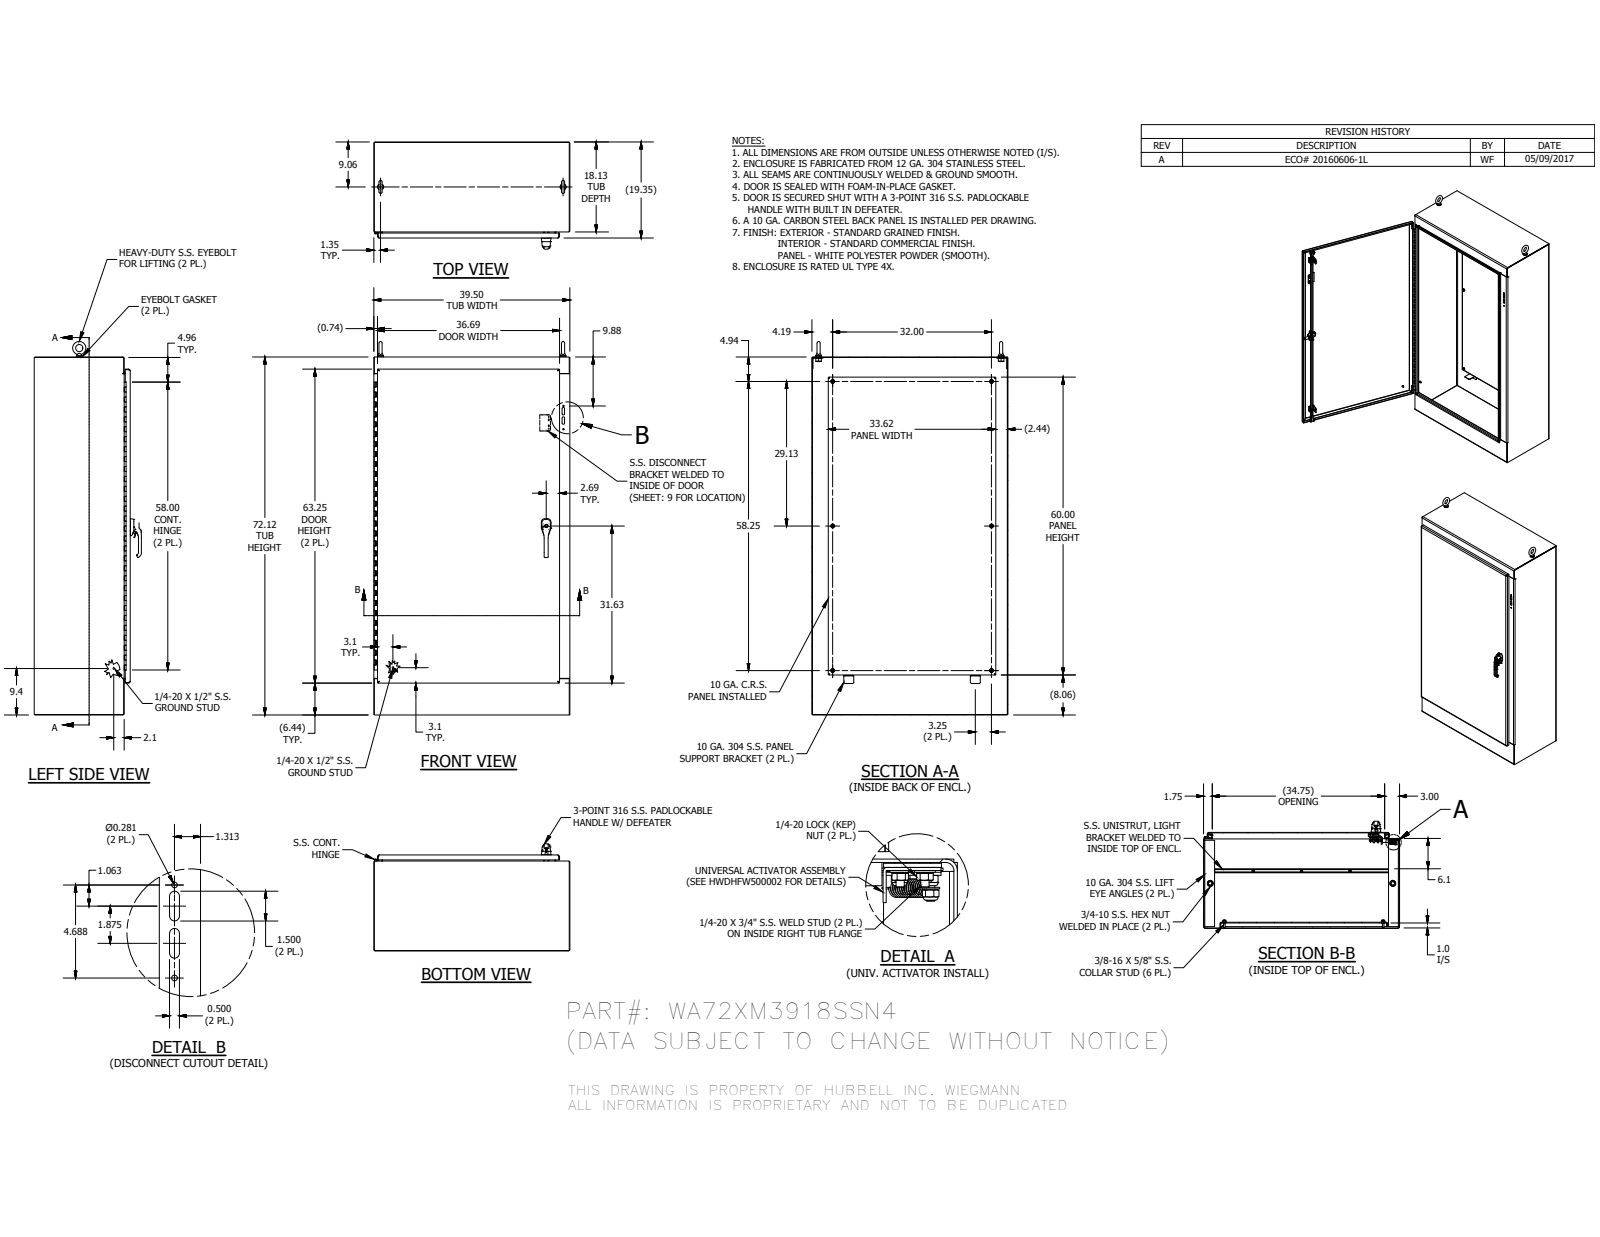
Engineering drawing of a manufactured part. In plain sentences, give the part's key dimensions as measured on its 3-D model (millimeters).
The part is named "WA72XM3918SSN4BLR; WAXM3918SSN4TOP; WAXM3918SSN4BTM; FUN00129_WAXM39SSN4 (+8 more)". Its 3-D file was written by "Autodesk Inventor 2016 (AUTOMOTIVE_DESIGN)". It is 126 solids with 4763 faces: 2197 planar, 1524 cylindrical and 1042 other. Overall it measures 1911.29 by 1003.3 by 548.55 millimeters. Its volume is 22 570 000 cubic millimeters and its surface area 16 220 000 square millimeters. Round holes: 24 of diameter 3.55, 10 of diameter 9.52, 9 of diameter 6.35, 8 of diameter 6.65, 6 of diameter 3.96, 6 of diameter 7.8, 6 of diameter 14.29, 5 of diameter 4.76, 4 of diameter 3.45, 4 of diameter 4.17, 4 of diameter 5.1, 4 of diameter 7.37. Round bosses or shafts: 10 of diameter 15.88, 9 of diameter 8.38, 6 of diameter 14.29, 4 of diameter 13.54, 4 of diameter 8.56, 4 of diameter 6.35, 4 of diameter 6.02, 3 of diameter 6. Partial cylindrical surfaces (rounded edges, fillets, slot ends): 187 of radius 0.5, 109 of radius 0.3, 48 of radius 0.51, 26 of radius 6.35, 21 of radius 0.47, 20 of radius 1.59, 18 of radius 3.17, 16 of radius 0.64. The main face-to-face distances are 2.64, 488.79, 1000.66, 486.15, 491.43, 3.41, 1829.34, 25.4, 998.02, 463.39. The hole center spacings are 0.45, 163.69, 1379.46, 0.59, 0.6, 9.65, 19.31, 327.38.
